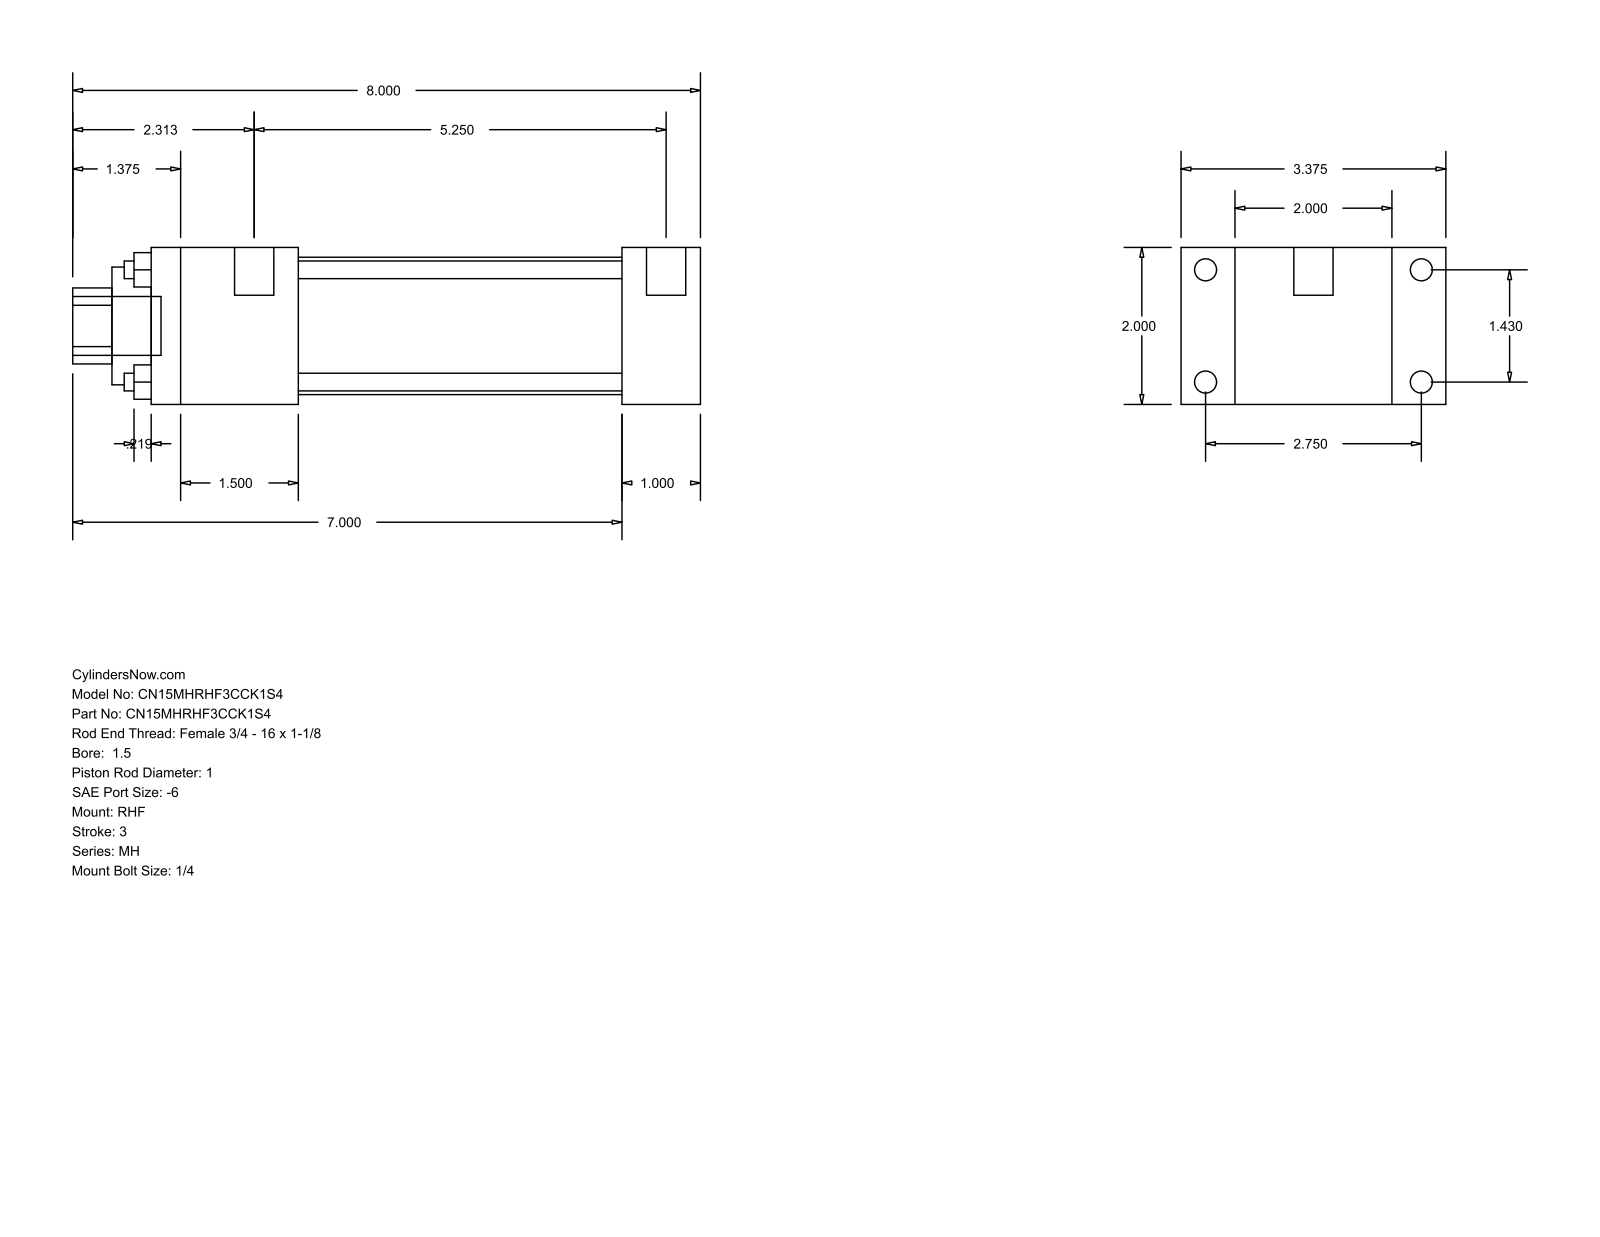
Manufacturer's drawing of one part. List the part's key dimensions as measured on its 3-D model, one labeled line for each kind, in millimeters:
Part name (STEP PRODUCT): MH_RHF__0150_1
STEP written by: GSSL Pune (CONFIG_CONTROL_DESIGN)
Units: millimetres
Bodies: 0 solids, 88 faces (60 planar, 28 cylindrical, 0 other)
Overall size (bounding box): 203.2 × 85.72 × 50.8
Round holes (diameter × count): ⌀5.71 ×4, ⌀25.4 ×1, ⌀38.1 ×1, ⌀44.45 ×1
Round bosses / shafts (diameter × count): ⌀7.14 ×4, ⌀5.56 ×4, ⌀12.7 ×2, ⌀19.05 ×1
Partial cylindrical surfaces — rounded edges, fillets, slot ends (radius × count): R12.29 ×1
Main face-to-face distances: 50.8, 25.4, 17.46, 68.26, 85.72, 177.8, 152.4, 47.63, 104.77, 130.17
Hole centre spacings: 25.68, 36.32, 51.36
